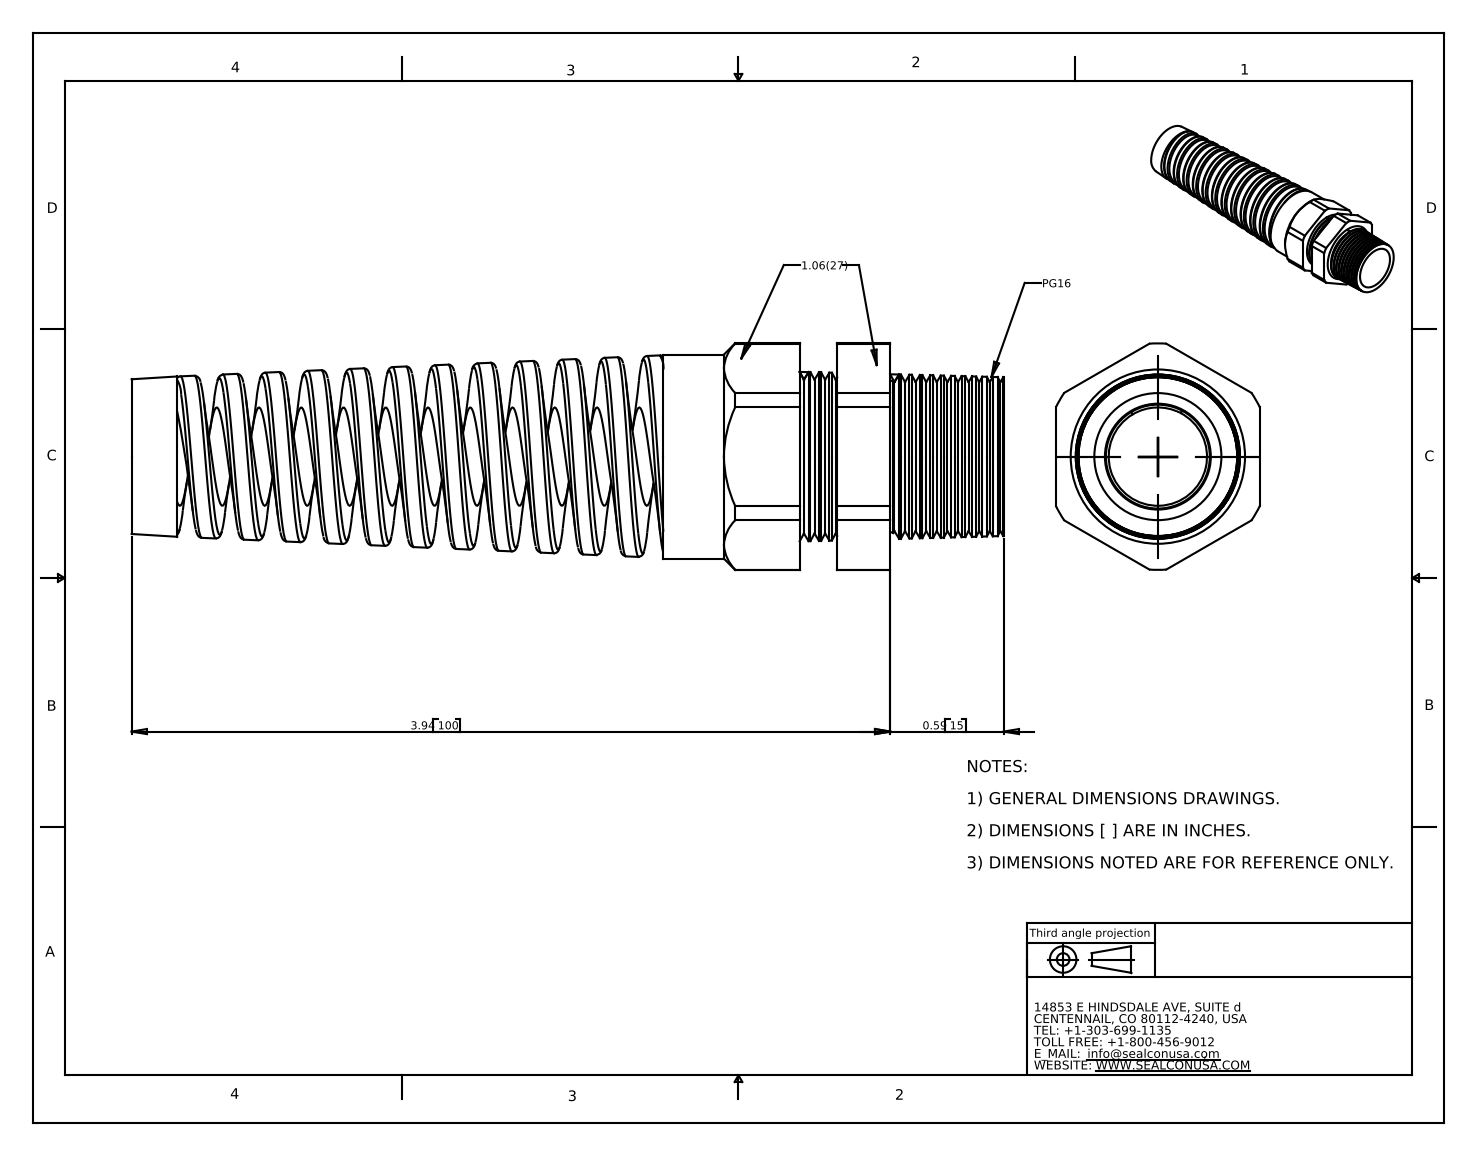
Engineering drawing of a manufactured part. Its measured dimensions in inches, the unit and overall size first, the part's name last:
Units: inches
Overall size (bounding box): 4.53 × 1.177 × 1.06
Round holes (diameter × count): ⌀0.511 ×1, ⌀0.54 ×1, ⌀0.55 ×1
Round bosses / shafts (diameter × count): ⌀1.06 ×1, ⌀0.66 ×1
Partial cylindrical surfaces — rounded edges, fillets, slot ends (radius × count): R0.588 ×1
Main face-to-face distances: 1.06, 0.194, 0.47, 0.276, 0.708, 0.902, 1.178, 2.762, 3.47, 3.665
Volume: 1.673 in³ · Surface area: 31.79 in²
Bodies: 2 solids, 210 faces (24 planar, 49 cylindrical, 137 other)
Part name (STEP PRODUCT): CF16CA-BK
STEP written by: SolidWorks 2007 (CONFIG_CONTROL_DESIGN)
